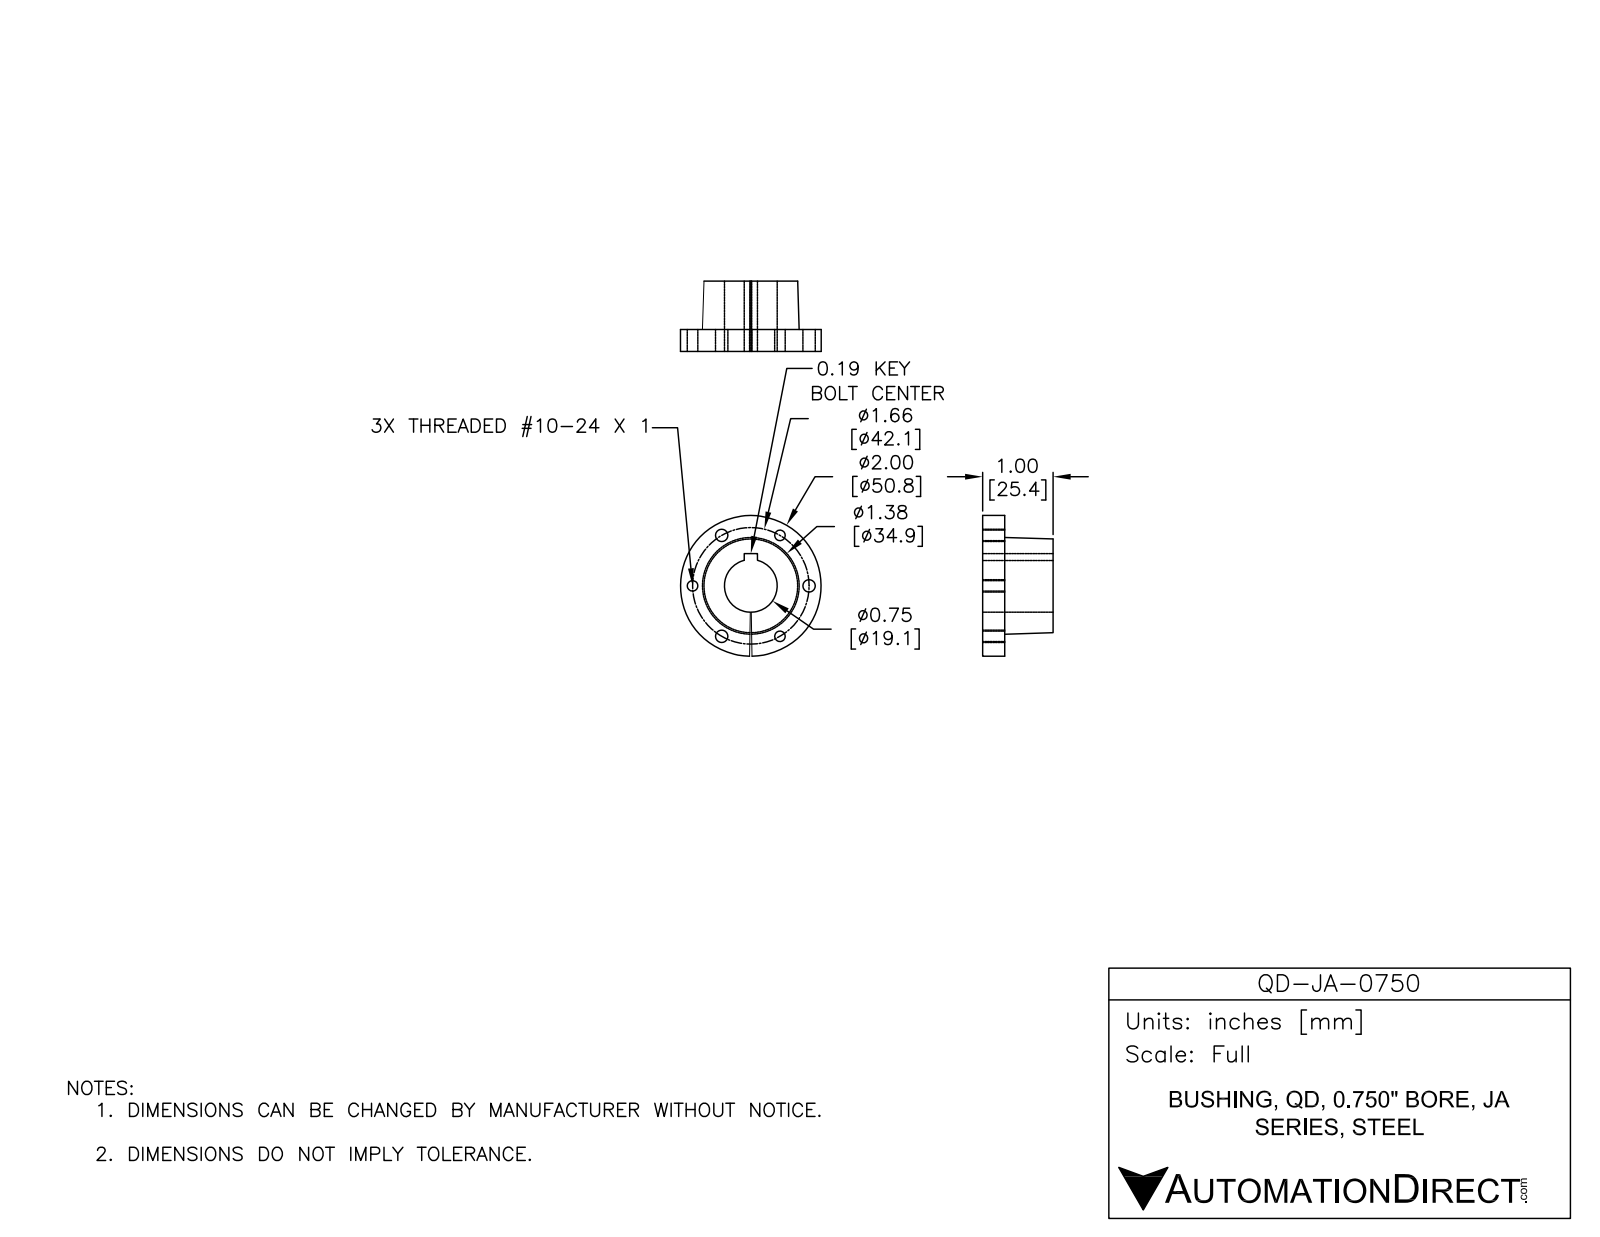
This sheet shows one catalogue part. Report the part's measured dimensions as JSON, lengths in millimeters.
{"part_name": "QD-JA-0750", "step_written_by": "SolidWorks 2014 (AUTOMOTIVE_DESIGN)", "units": "millimeters", "bodies": {"solids": 1, "faces": 29, "planar": 8, "cylindrical": 18, "other": 3}, "overall_size": [50.8, 50.8, 25.4], "volume_mm3": 23990, "surface_area_mm2": 9142, "round_holes": [[3.8, 3], [4.4, 3], [19.1, 1]], "round_bosses_or_shafts": [[50.8, 1]], "face_to_face_distances": [8, 25.4, 17.4, 4.7], "hole_center_spacings": [21, 21, 36.4, 36.4, 42.1, 42.1]}
